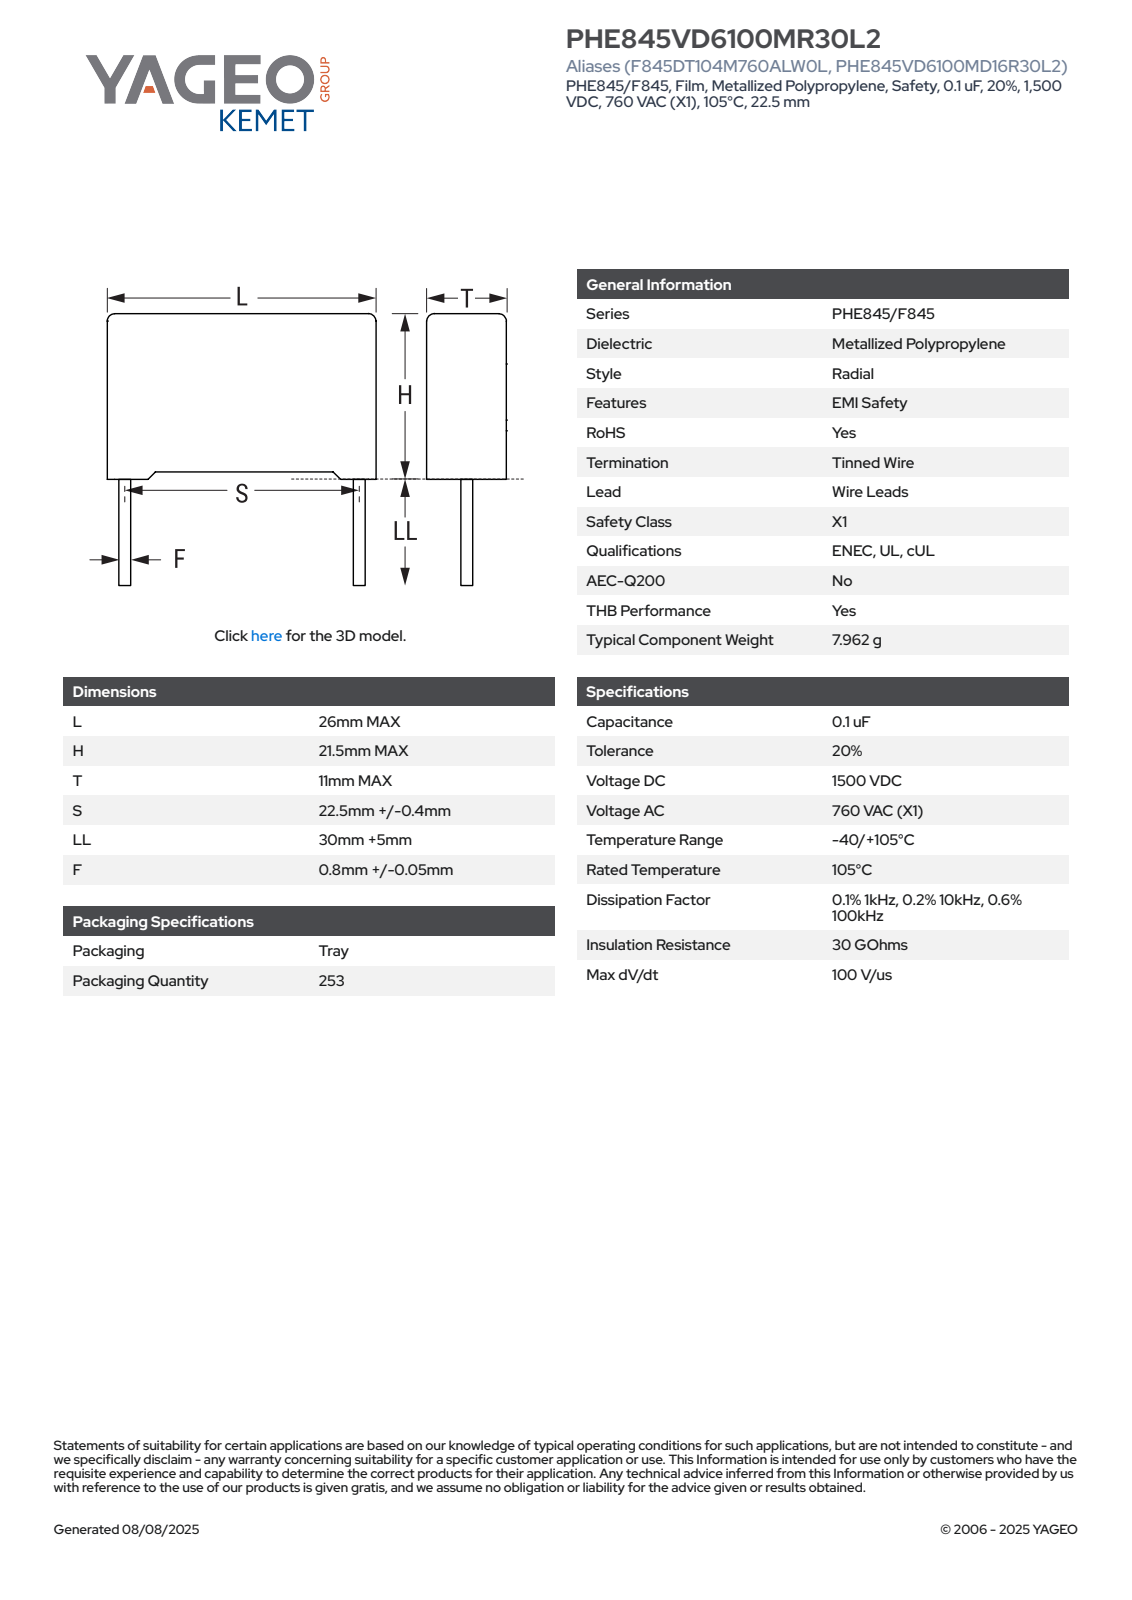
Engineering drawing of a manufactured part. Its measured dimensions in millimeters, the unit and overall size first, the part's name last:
Units: millimetres
Overall size (bounding box): 56.5 × 26 × 11.01
Round bosses / shafts (diameter × count): ⌀0.8 ×2
Partial cylindrical surfaces — rounded edges, fillets, slot ends (radius × count): R0.5 ×4
Main face-to-face distances: 11, 26, 20.75, 20.76, 0.74, 0.75, 21.5, 0.87, 25.13, 10.13
Volume: 5 988 mm³ · Surface area: 2 373 mm²
Bodies: 4 solids, 85 faces (77 planar, 8 cylindrical, 0 other)
Part name (STEP PRODUCT): CFR_RB2_26X21.5X11_L26H21.5T11S22.5LL35F0.8
STEP written by: SolidWorks 2021 (AUTOMOTIVE_DESIGN)
